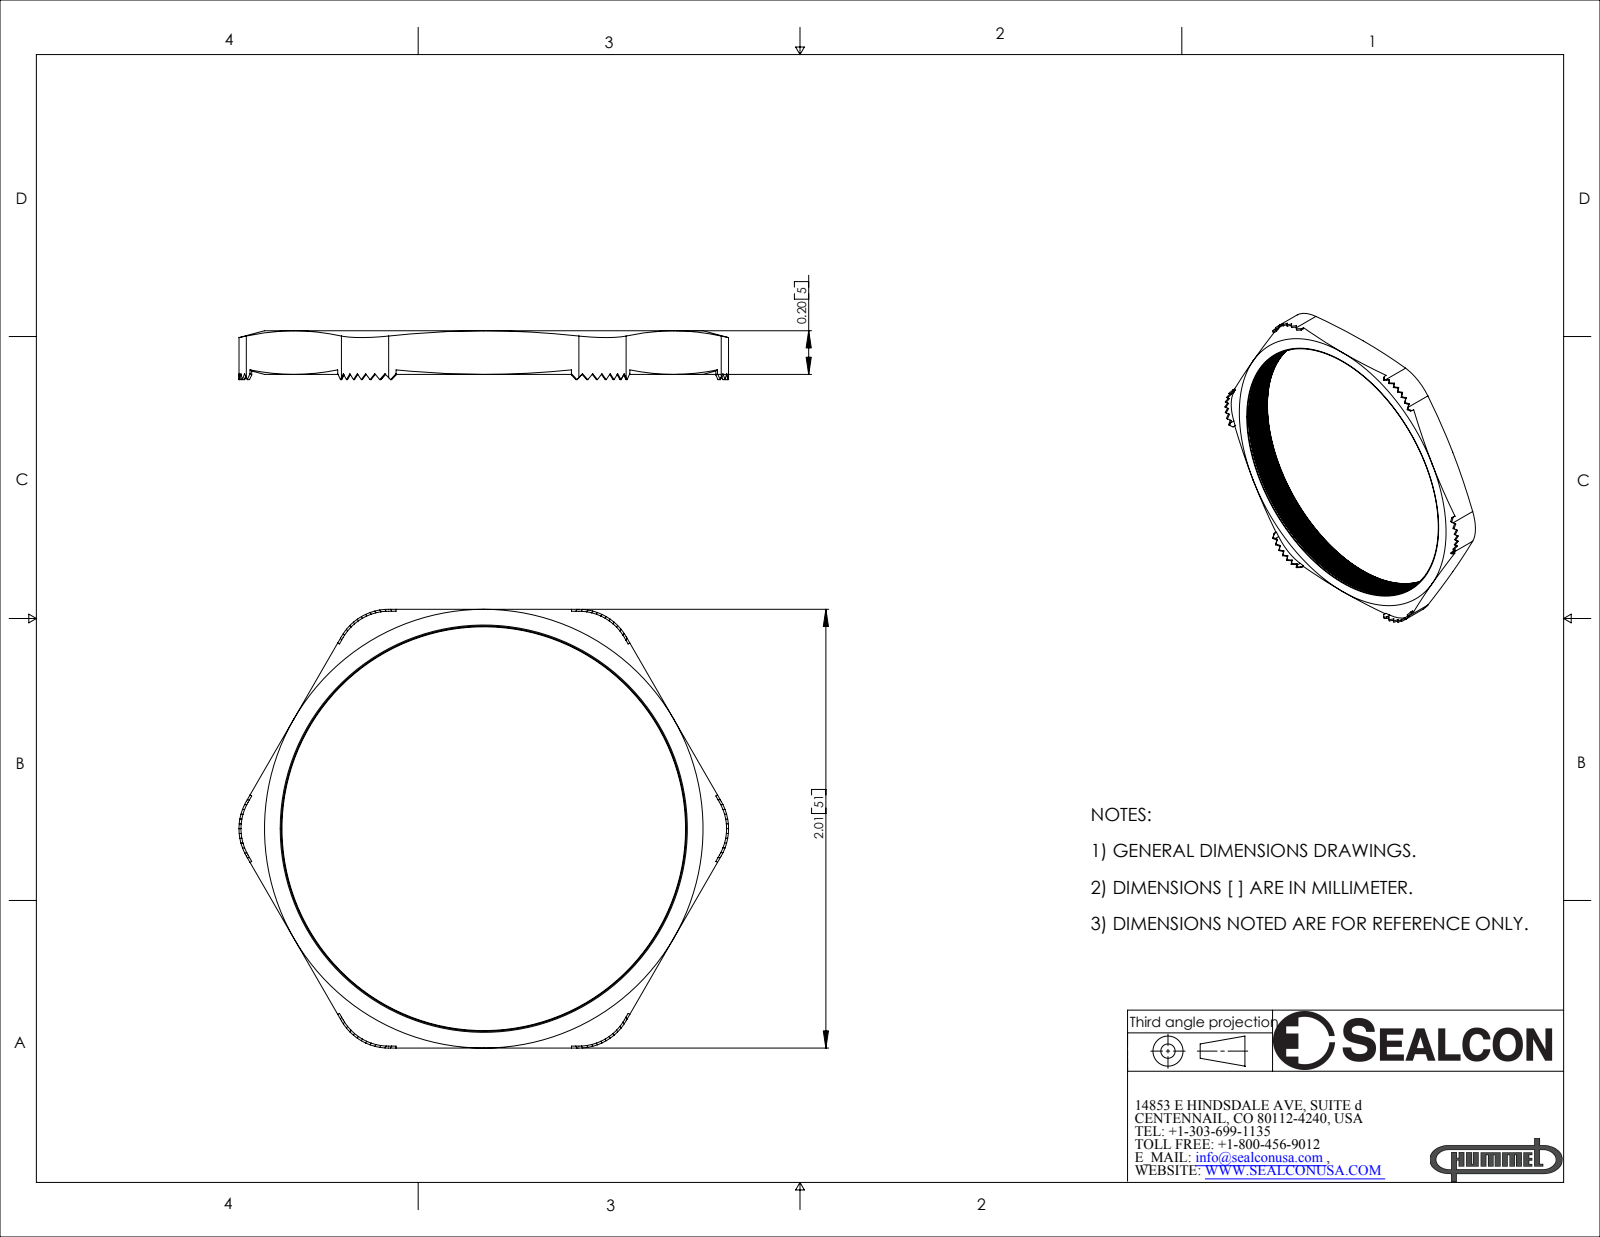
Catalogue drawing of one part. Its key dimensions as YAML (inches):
part_name: "NP-36-BE"
step_written_by: "SolidWorks 2007 (CONFIG_CONTROL_DESIGN)"
units: inches
bodies: {solids: 1, faces: 248, planar: 116, cylindrical: 46, other: 86}
overall_size: [2.244, 2.01, 0.224]
volume: 0.146
surface_area: 5.163
round_holes:
  - {diameter: 1.85, count: 1}
partial_cylinders:
  - {radius: 0.241, count: 6}
  - {radius: 0.25, count: 6}
face_to_face_distances: [2.01, 0.2, 0.034, 2.001, 0.069, 0.069, 0.035, 0.103, 0.103, 1.992]
